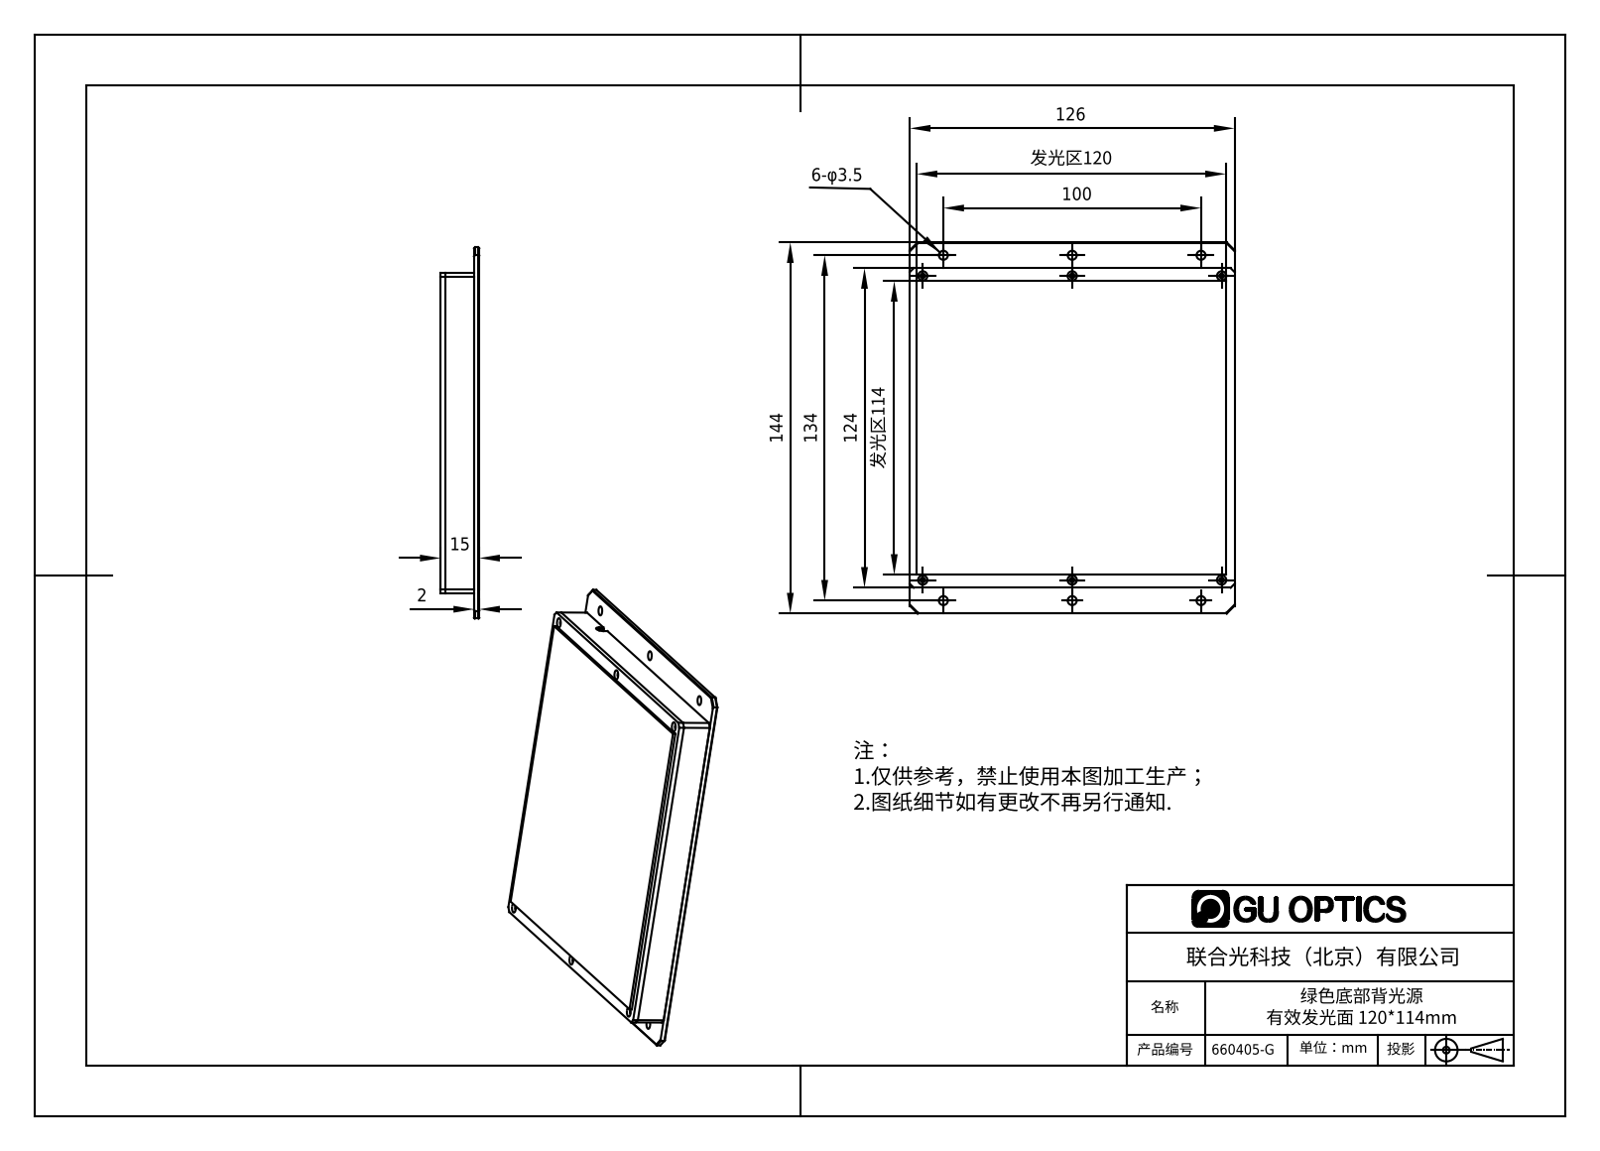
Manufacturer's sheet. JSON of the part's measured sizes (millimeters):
{"part_name": "660405-G", "step_written_by": "SolidWorks 2016 (AUTOMOTIVE_DESIGN)", "units": "millimeters", "bodies": {"solids": 4, "faces": 2126, "planar": 1933, "cylindrical": 86, "other": 107}, "overall_size": [144, 126, 16], "volume_mm3": 115243, "surface_area_mm2": 113647, "round_holes": [[1.25, 6], [1.6, 6], [1.8, 6], [2, 6], [2.4, 6], [3.5, 6]], "partial_cylinders_radius": [[1, 4], [1.5, 4], [2, 2], [1.6, 1]], "face_to_face_distances": [13, 3, 2, 11, 14, 16, 1, 10, 13.03, 10.03], "hole_center_spacings": [58, 116, 131.93, 0.5, 118.5, 10.97, 11.31, 50]}
